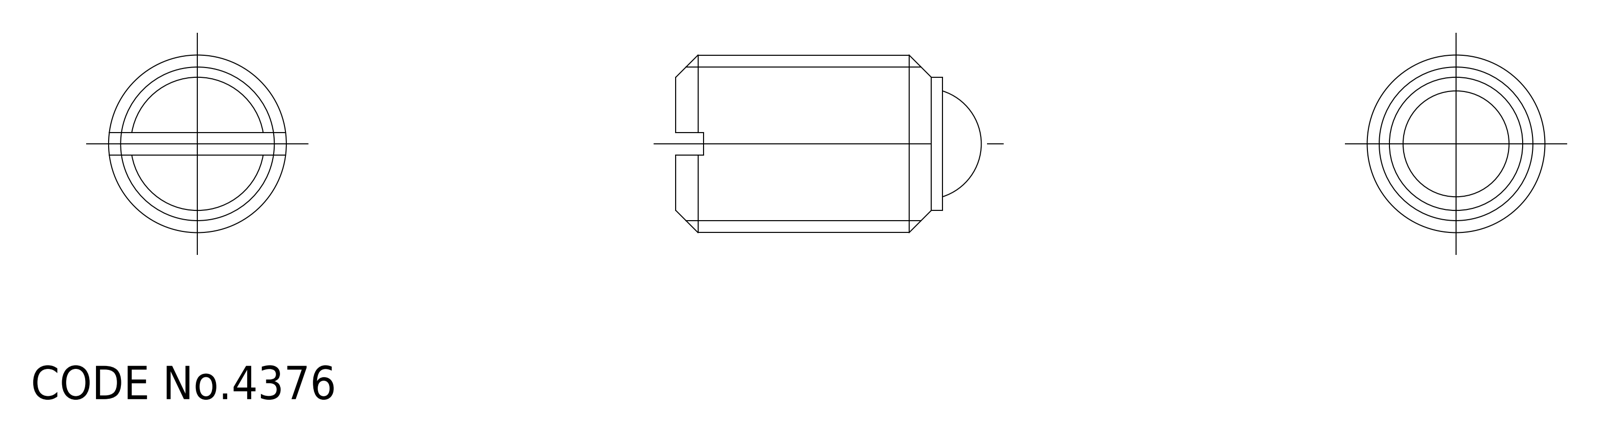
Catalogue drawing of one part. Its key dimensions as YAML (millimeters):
part_name: "ball; PBF_16_KN_14064_36"
step_written_by: "CADfix (AUTOMOTIVE_DESIGN)"
units: millimeters
bodies: {solids: 2, faces: 19, planar: 0, cylindrical: 0, other: 19}
overall_size: [27.5, 16, 16]
volume: 4113
surface_area: 2210
